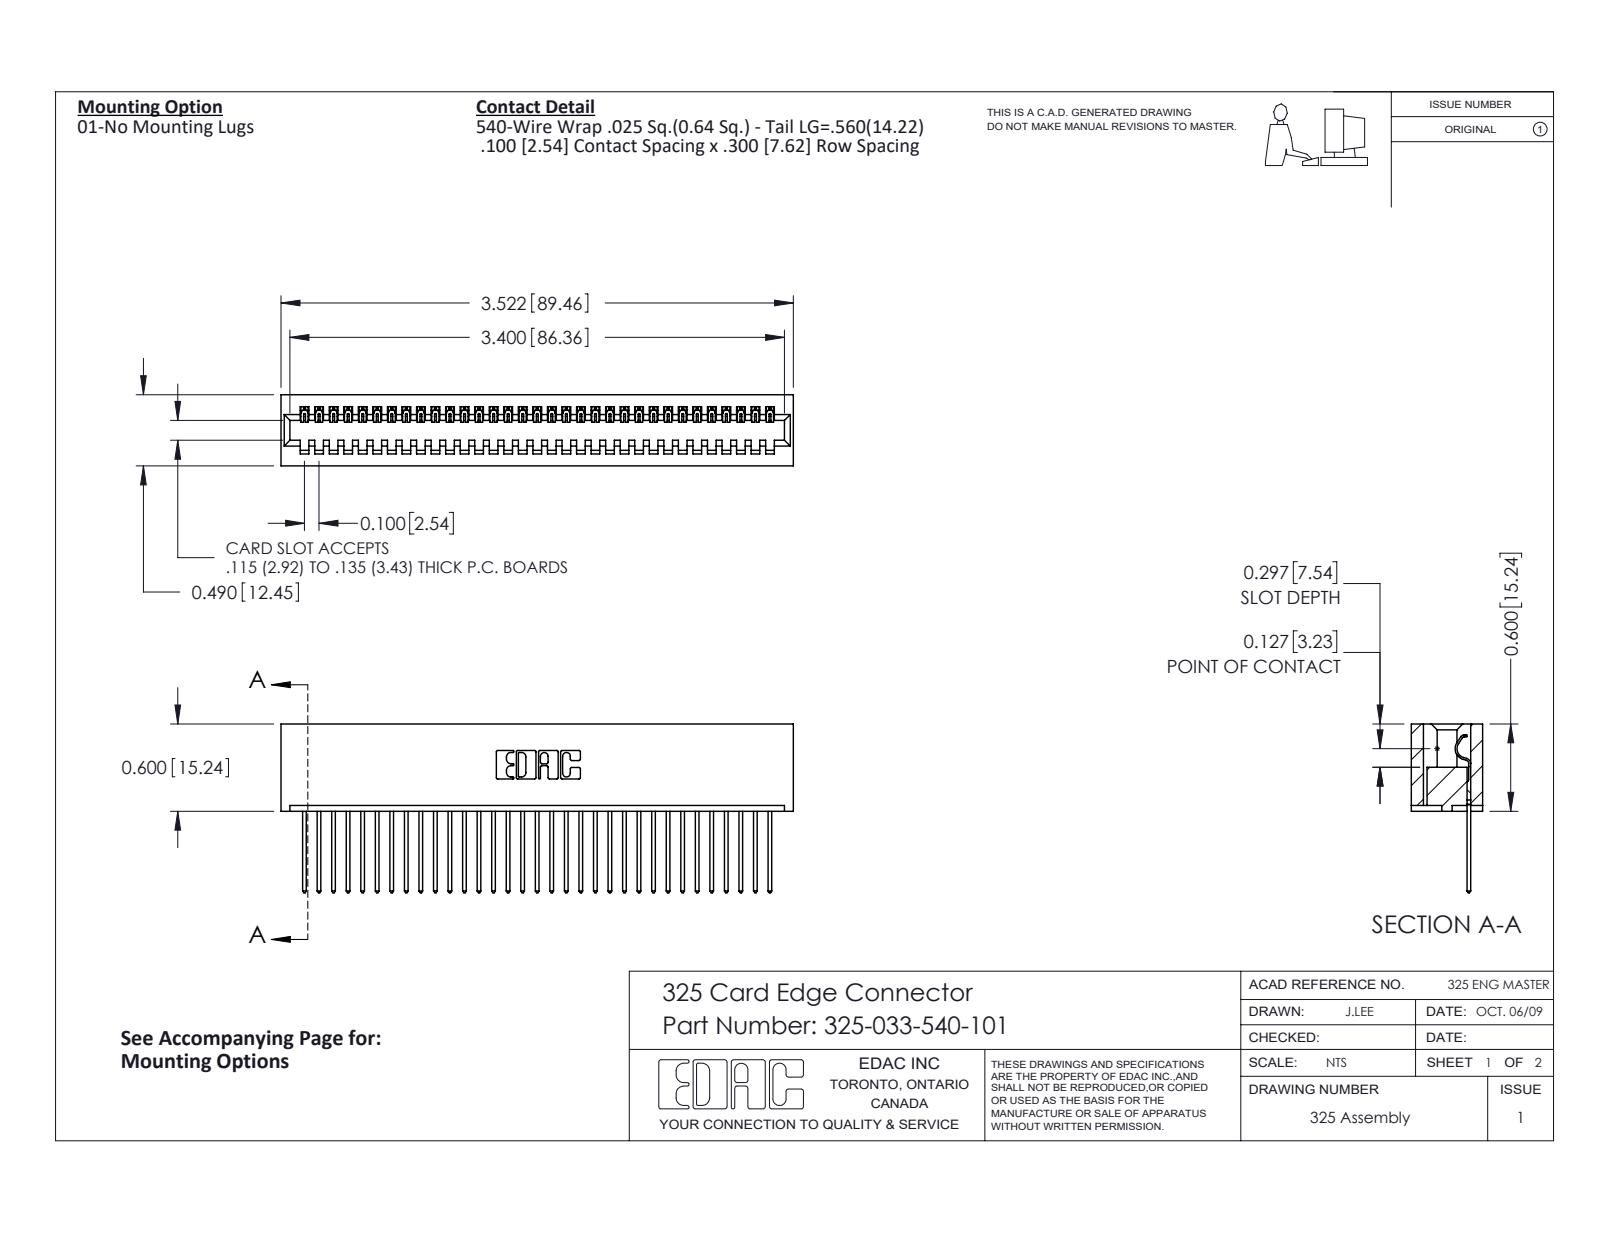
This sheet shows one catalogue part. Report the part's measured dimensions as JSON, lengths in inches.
{"part_name": "325 Part_Lugless; 325-292-001_325-293-140; 325-033-540-101", "step_written_by": "SolidWorks 2016 (CONFIG_CONTROL_DESIGN)", "units": "inches", "bodies": {"solids": 34, "faces": 2020, "planar": 1452, "cylindrical": 568, "other": 0}, "overall_size": [3.522, 1.16, 0.49], "volume_in3": 0.726, "surface_area_in2": 21.19, "partial_cylinders_radius": [[0.006, 66], [0.01, 66], [0.01, 22], [0.007, 6], [0.031, 6], [0.026, 3], [0.014, 1], [0.022, 1]], "face_to_face_distances": [0.083, 0.407, 0.3, 0.49, 0.107, 0.383, 0.025, 0.325, 0.56, 0.263]}
